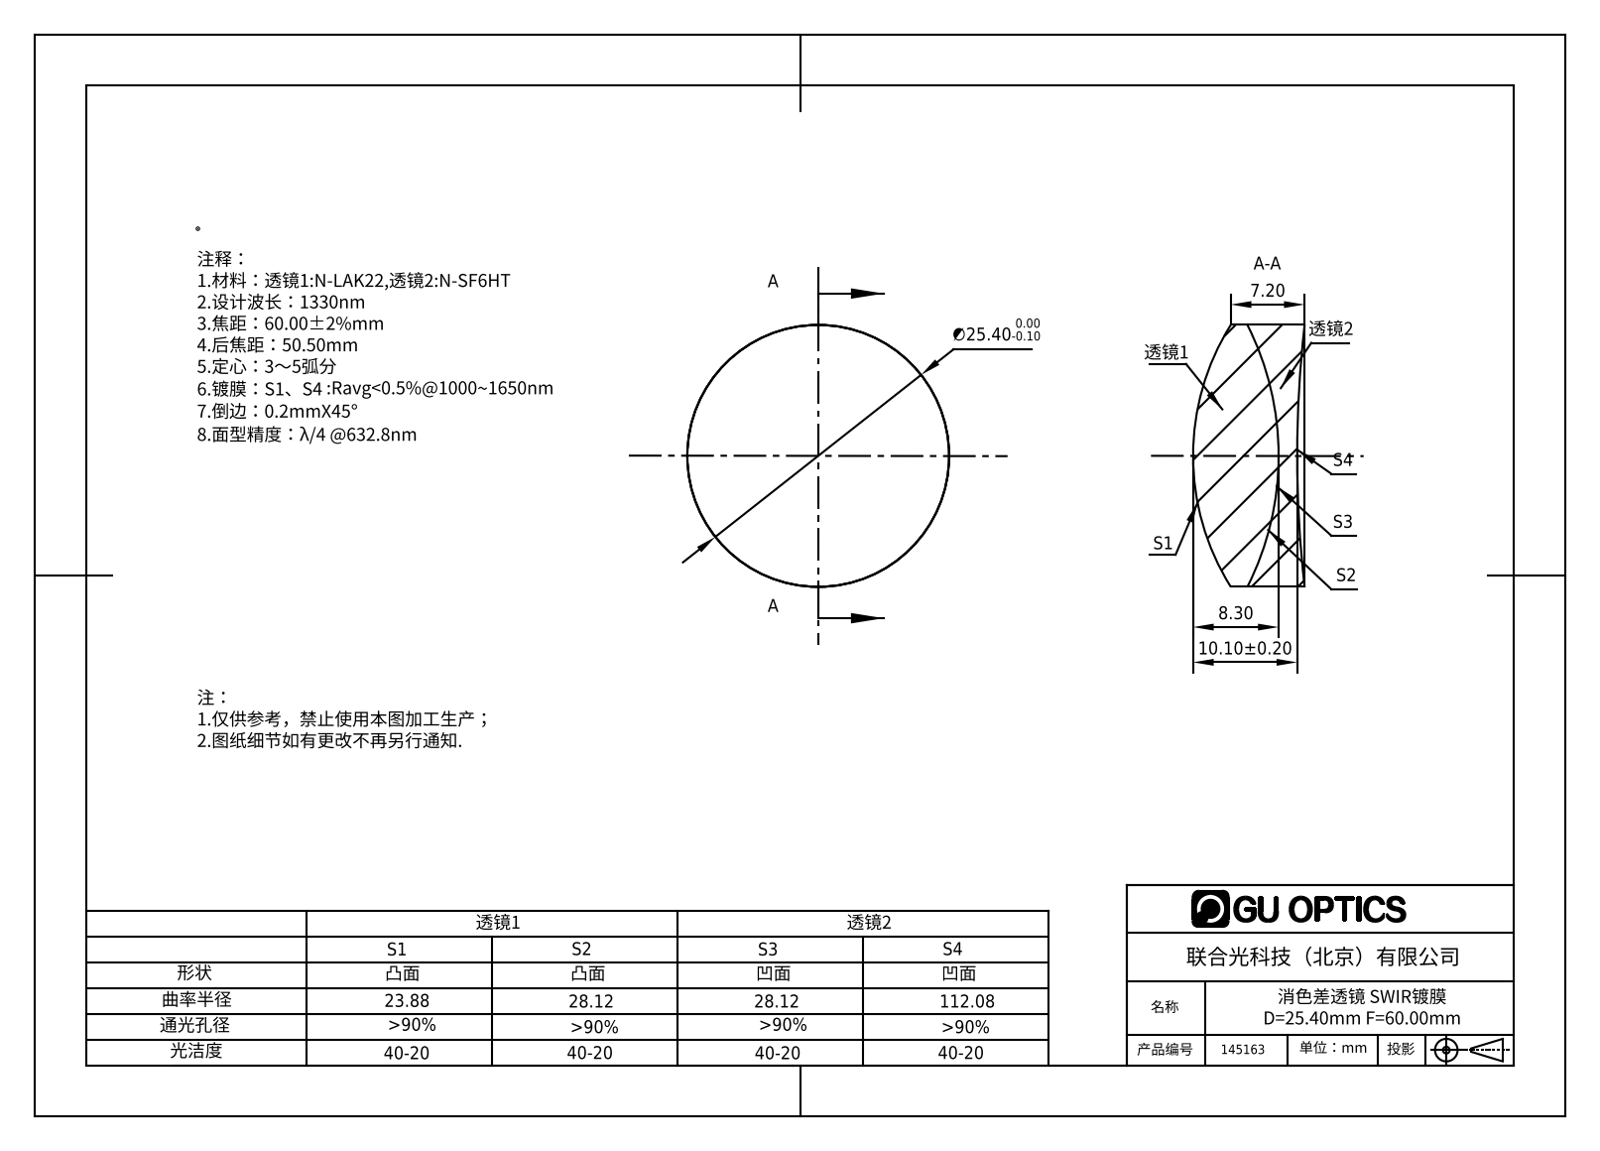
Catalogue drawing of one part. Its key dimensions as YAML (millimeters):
part_name: "145163"
step_written_by: "SolidWorks 2016 (AUTOMOTIVE_DESIGN)"
units: millimeters
bodies: {solids: 2, faces: 12, planar: 0, cylindrical: 4, other: 8}
overall_size: [25.4, 25.4, 10.82]
volume: 4399
surface_area: 2700
round_bosses_or_shafts:
  - {diameter: 25.4, count: 1}
